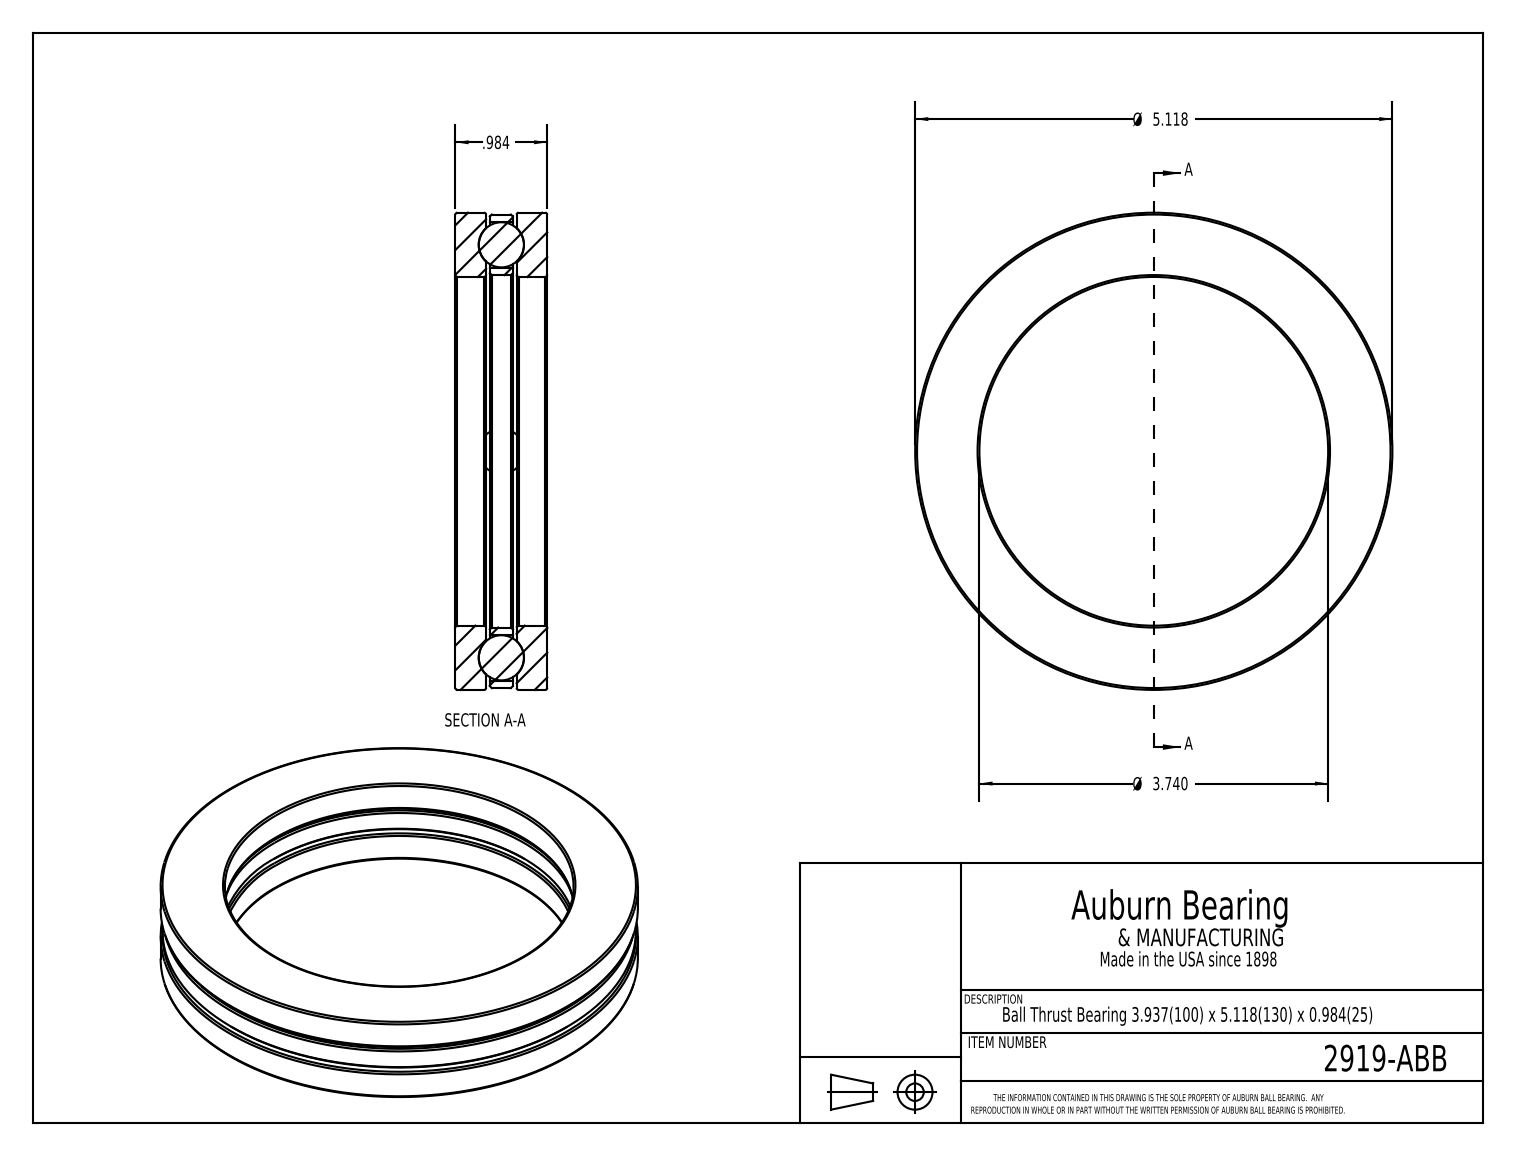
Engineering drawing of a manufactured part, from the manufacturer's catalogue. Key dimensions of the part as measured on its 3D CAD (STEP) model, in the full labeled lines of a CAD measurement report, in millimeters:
Part name (STEP PRODUCT): 2919-ABB
STEP written by: SolidWorks 2017 (CONFIG_CONTROL_DESIGN)
Units: millimetres
Bodies: 7 solids, 36 faces (8 planar, 10 cylindrical, 18 other)
Overall size (bounding box): 130 × 130 × 25
Volume: 113 300 mm³ · Surface area: 49 970 mm²
Round holes (diameter × count): ⌀12.5 ×4, ⌀100 ×1, ⌀101 ×1
Round bosses / shafts (diameter × count): ⌀130 ×1, ⌀129 ×1
Main face-to-face distances: 9.4, 15.6, 25, 6.2, 8.3, 16.7, 1, 7.3, 8.3
Hole centre spacings: 57.5, 81.3, 115
